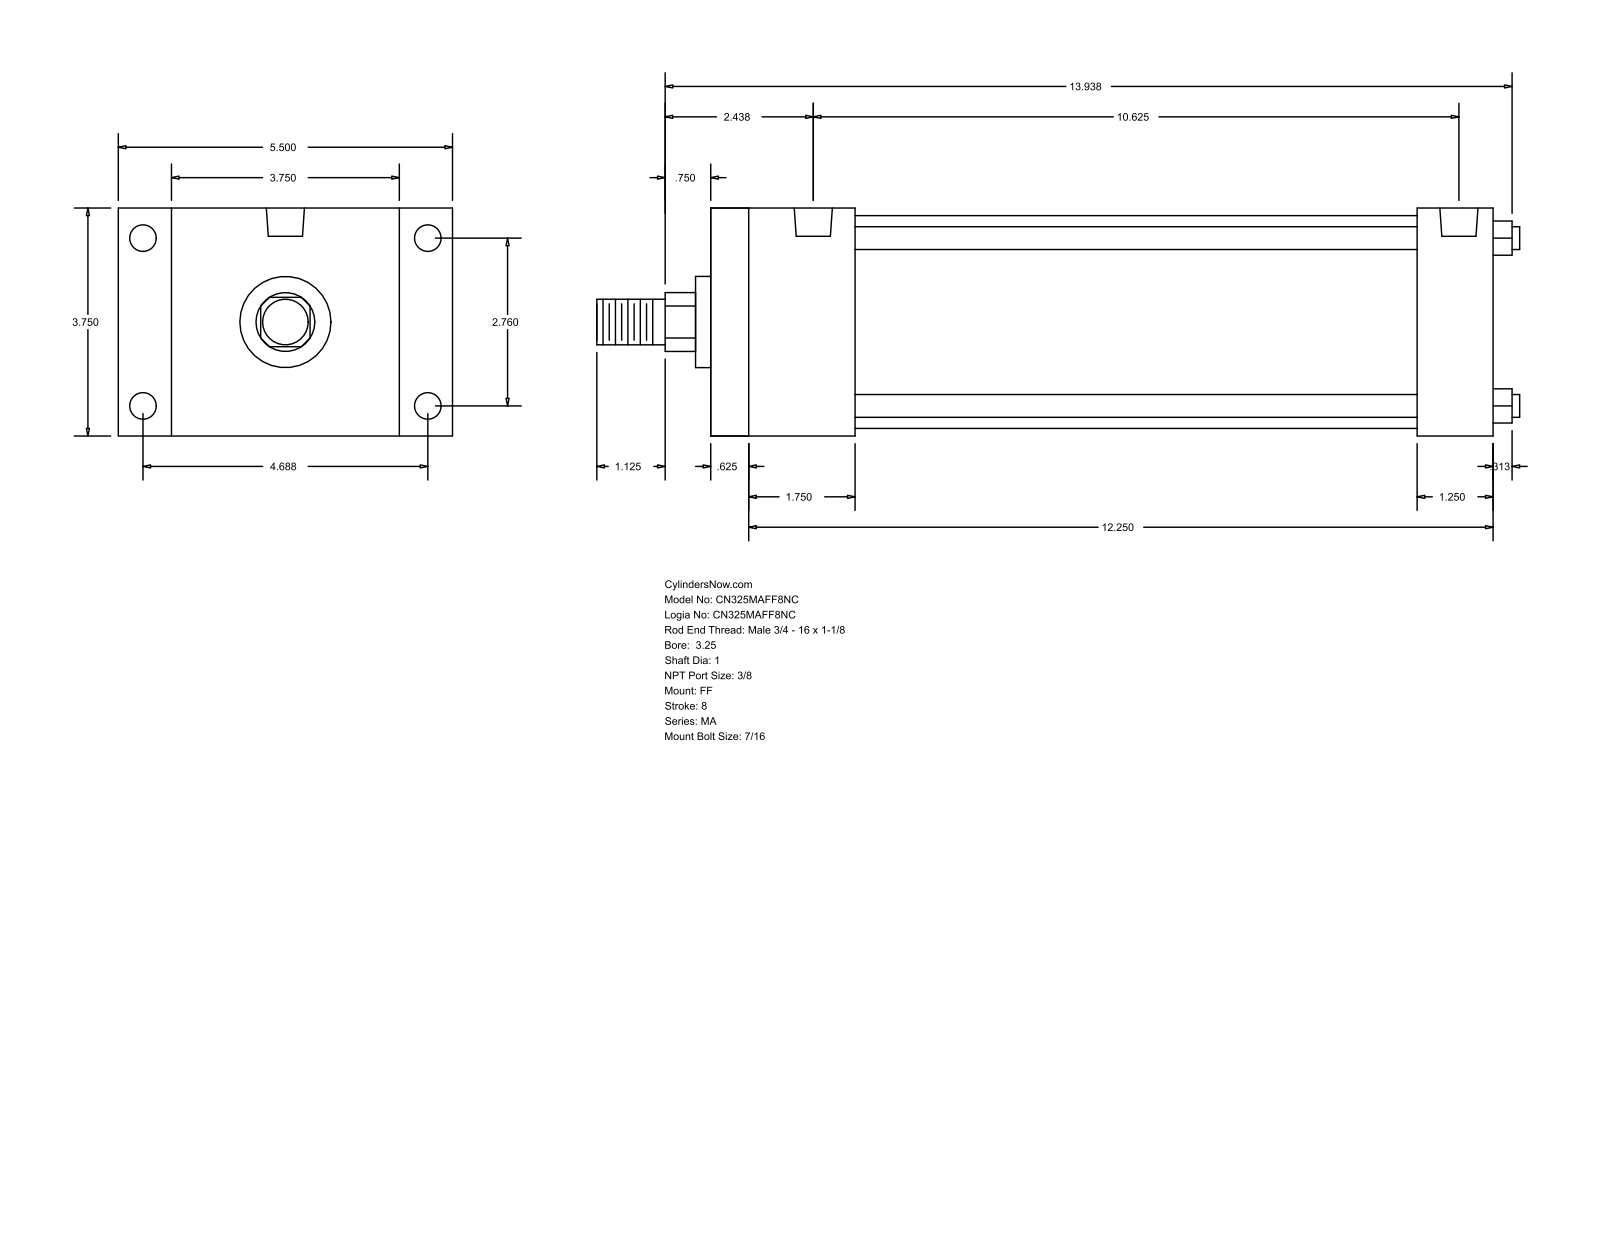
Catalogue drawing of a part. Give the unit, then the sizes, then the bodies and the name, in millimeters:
Units: millimetres
Overall size (bounding box): 385.76 × 139.7 × 95.25
Round holes (diameter × count): ⌀11.11 ×8, ⌀15.93 ×2
Round bosses / shafts (diameter × count): ⌀9.53 ×4, ⌀88.9 ×1, ⌀38.1 ×1, ⌀25.4 ×1, ⌀19.05 ×1
Partial cylindrical surfaces — rounded edges, fillets, slot ends (radius × count): R12.29 ×1
Main face-to-face distances: 95.24, 327.02, 15.87, 311.15, 22.23, 117.47, 60.33, 295.27, 44.46, 279.4
Hole centre spacings: 70.1, 119.06, 138.16, 260.35, 4.76, 4.77, 265.11, 265.12
Bodies: 0 solids, 92 faces (64 planar, 28 cylindrical, 0 other)
Part name (STEP PRODUCT): MA_FF__0325_1
STEP written by: GSSL Pune (CONFIG_CONTROL_DESIGN)
